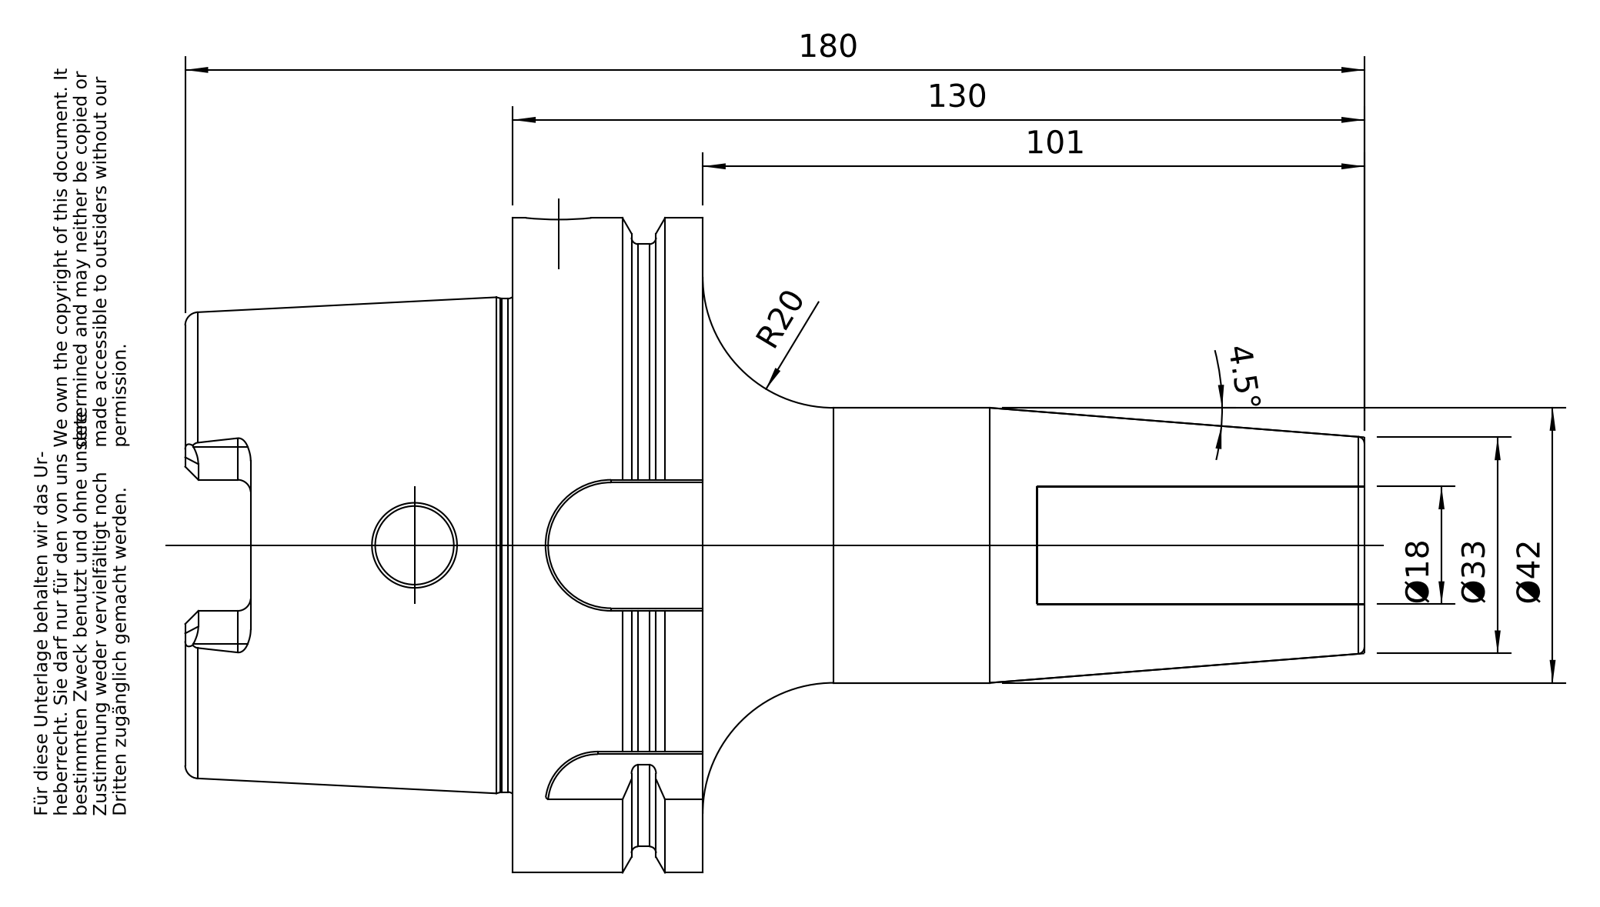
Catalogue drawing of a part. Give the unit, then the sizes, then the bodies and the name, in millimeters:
Units: millimetres
Overall size (bounding box): 180 × 100 × 100
Round holes (diameter × count): ⌀10 ×1, ⌀12 ×1, ⌀18 ×1, ⌀22.5 ×1, ⌀24 ×1, ⌀24.32 ×1, ⌀24.5 ×1, ⌀53 ×1, ⌀63 ×1
Round bosses / shafts (diameter × count): ⌀100 ×1, ⌀92 ×1, ⌀75.36 ×1, ⌀42 ×1
Partial cylindrical surfaces — rounded edges, fillets, slot ends (radius × count): R2 ×6, R5 ×4, R8 ×1, R10 ×1, R11 ×1
Main face-to-face distances: 29, 12.5, 16.5, 50, 62.5, 79, 130, 180, 117.5, 101
Volume: 379 371 mm³ · Surface area: 64 081 mm²
Bodies: 1 solid, 174 faces (50 planar, 51 cylindrical, 73 other)
Part name (STEP PRODUCT): A100-144-18
STEP written by: PRO/ENGINEER BY PARAMETRIC TECHNOLOGY CORPORATION, 2010430 (CONFIG_CONTROL_DESIGN)
